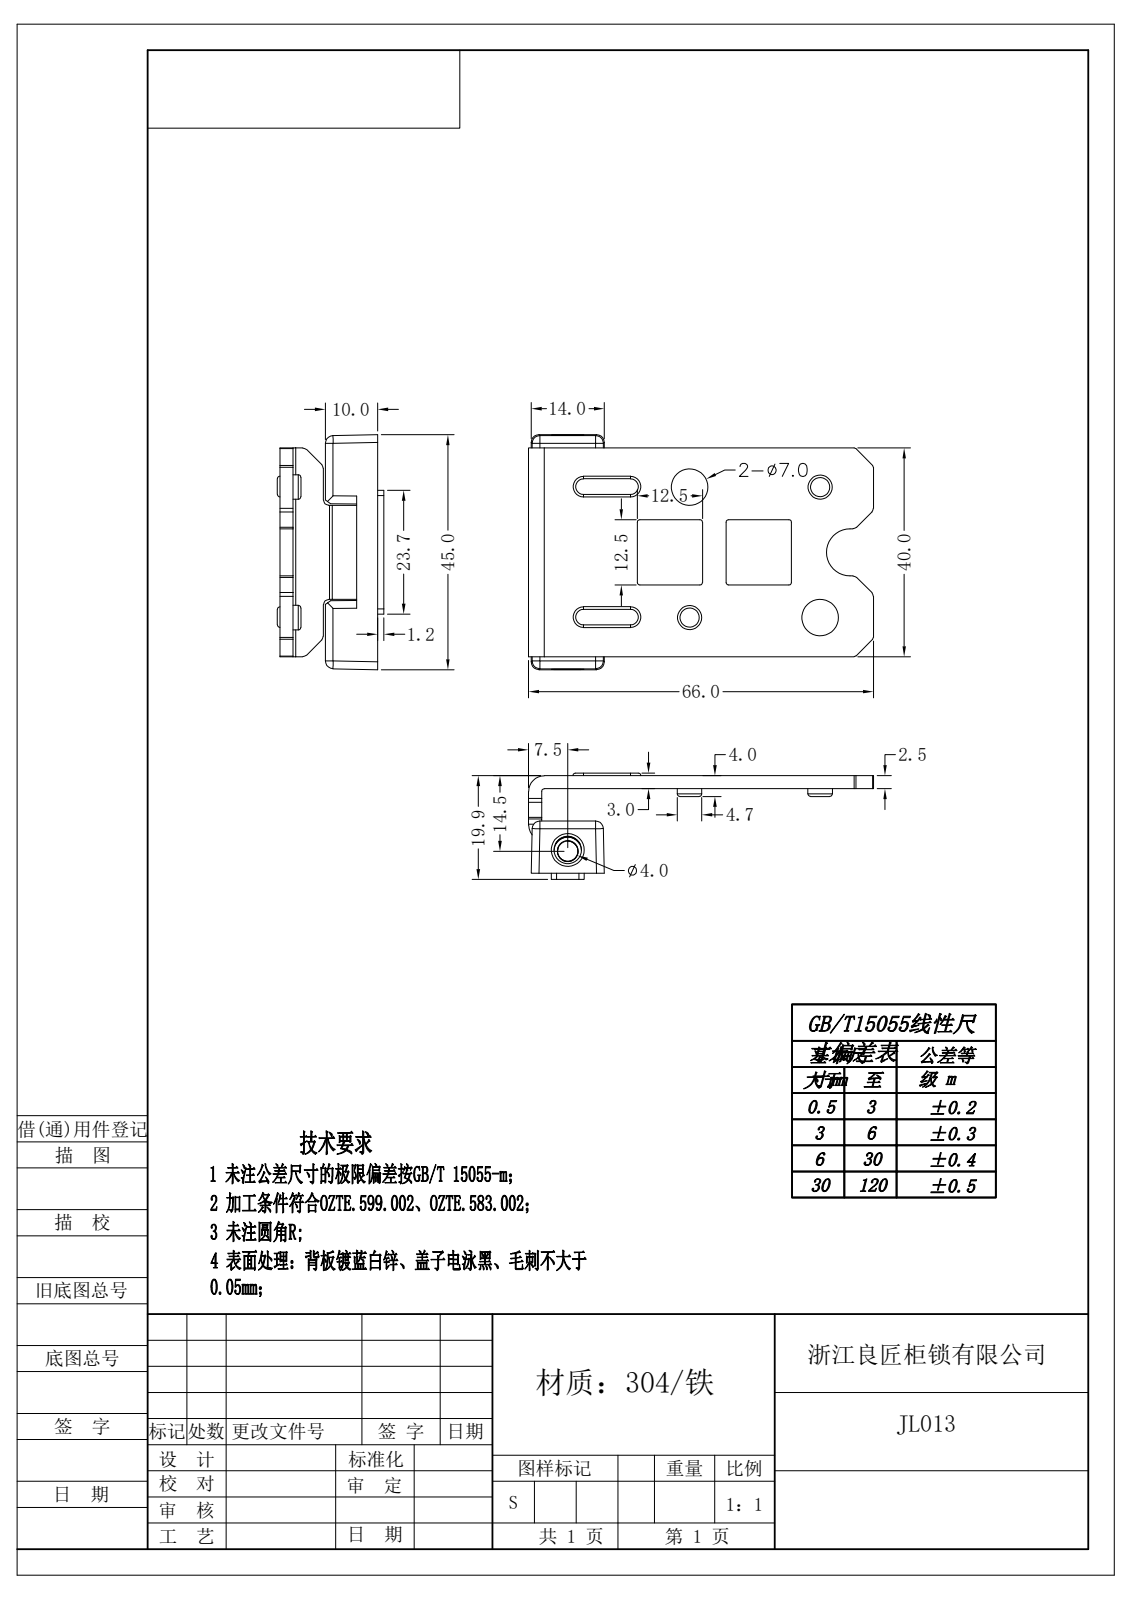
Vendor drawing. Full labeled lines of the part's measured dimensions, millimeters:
STEP written by: Rhino 8.5 (CONFIG_CONTROL_DESIGN)
Units: millimetres
Bodies: 2 solids, 231 faces (68 planar, 99 cylindrical, 64 other)
Overall size (bounding box): 66 × 45 × 21.2
Volume: 11 156 mm³ · Surface area: 9 414 mm²
Round holes (diameter × count): ⌀5 ×3, ⌀3.12 ×2, ⌀7 ×2, ⌀4 ×1
Partial cylindrical surfaces — rounded edges, fillets, slot ends (radius × count): R1 ×16, R1.5 ×16, R0.5 ×12, R0.35 ×8, R3.5 ×2, R2.05 ×1, R4.5 ×1, R4.55 ×1
Main face-to-face distances: 2.5, 17, 19.5, 10, 7, 9.5, 14, 15.5, 2, 16
Hole centre spacings: 22.46, 34, 35.36, 36.78, 47.21, 55.5
